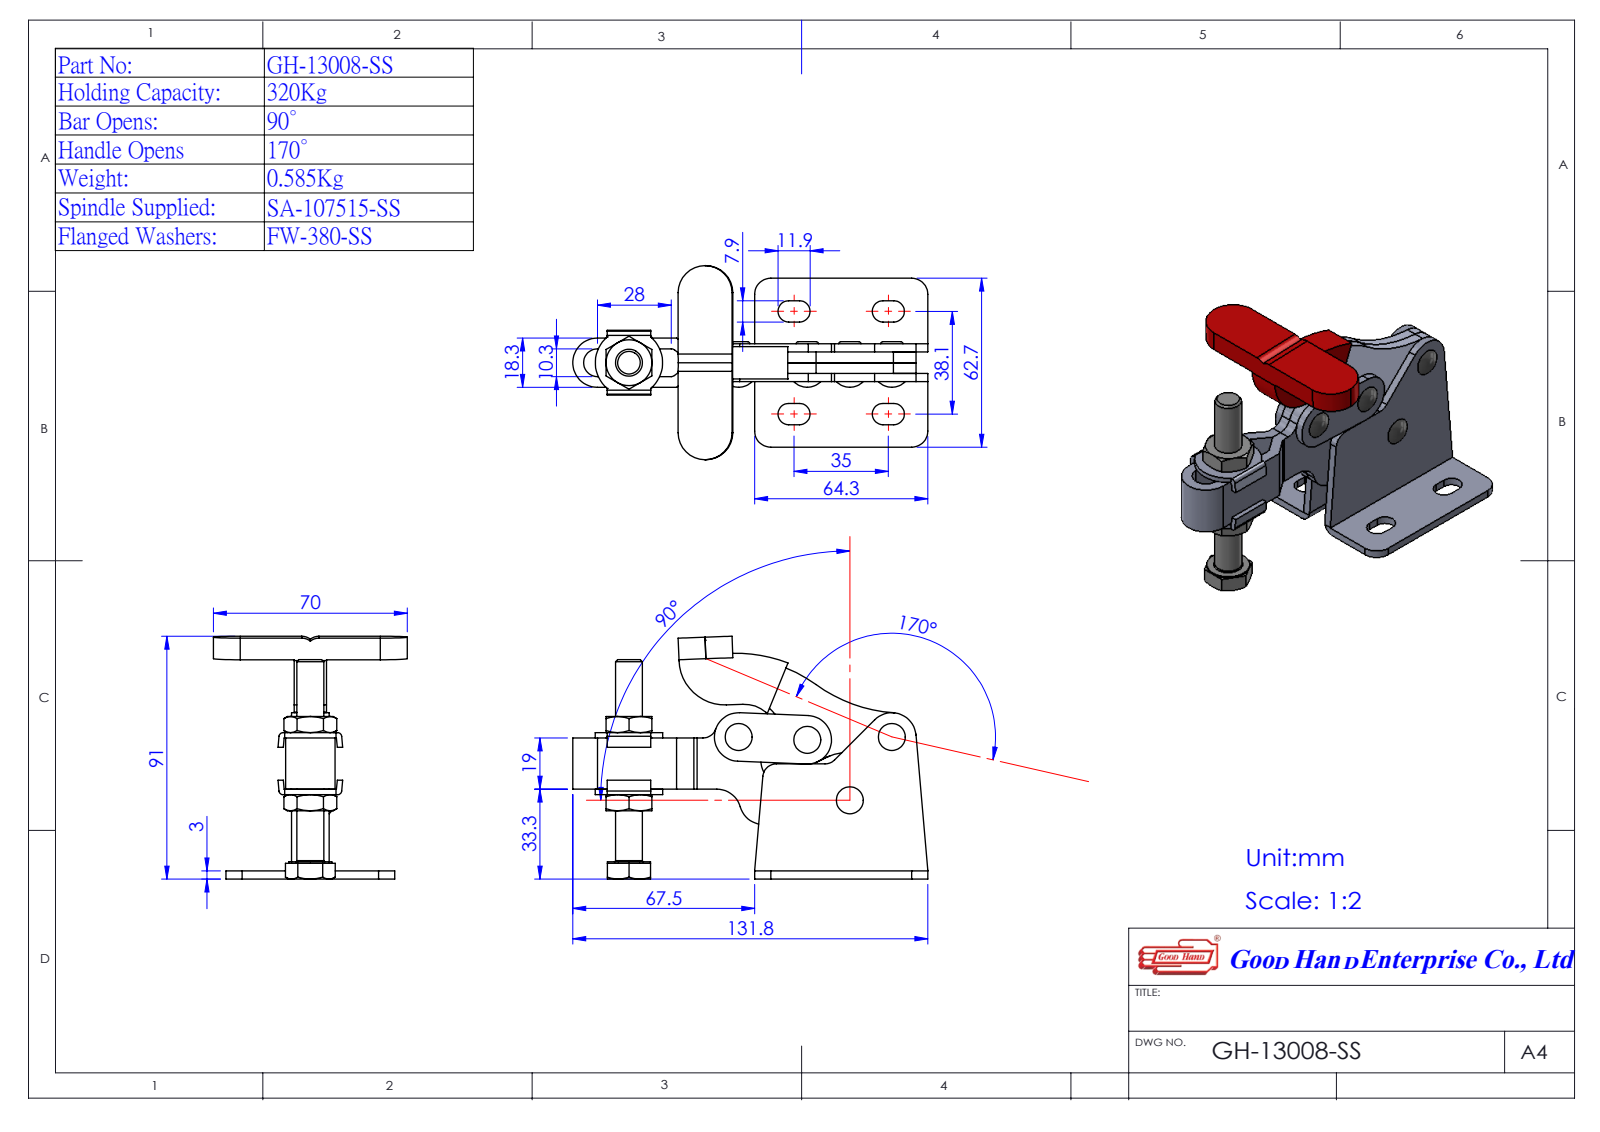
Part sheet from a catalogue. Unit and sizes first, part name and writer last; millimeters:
Units: millimetres
Overall size (bounding box): 131.8 × 90.09 × 72
Round holes (diameter × count): ⌀5 ×4
Round bosses / shafts (diameter × count): ⌀6.5 ×4, ⌀16 ×1, ⌀10 ×1
Partial cylindrical surfaces — rounded edges, fillets, slot ends (radius × count): R4 ×8, R9 ×8, R1.5 ×4, R2 ×4, R6 ×4, R5 ×3, R3.2 ×2, R3.3 ×2
Main face-to-face distances: 4, 3, 8, 7, 11, 2, 1.9, 6, 14, 4.1
Hole centre spacings: 25.51, 27.43, 28.2, 31.4, 47.5, 56.87
Volume: 87 096 mm³ · Surface area: 60 510 mm²
Bodies: 5 solids, 345 faces (165 planar, 128 cylindrical, 52 other)
Part name (STEP PRODUCT): 11300808-1^GH-13008-SS(簡化); 11300801-1^GH-13008-SS(簡化); Group5^GH-13008-SS(簡化); Group4^GH-13008-SS(簡化) (+2 more)
STEP written by: SolidWorks 2016 (AUTOMOTIVE_DESIGN)
